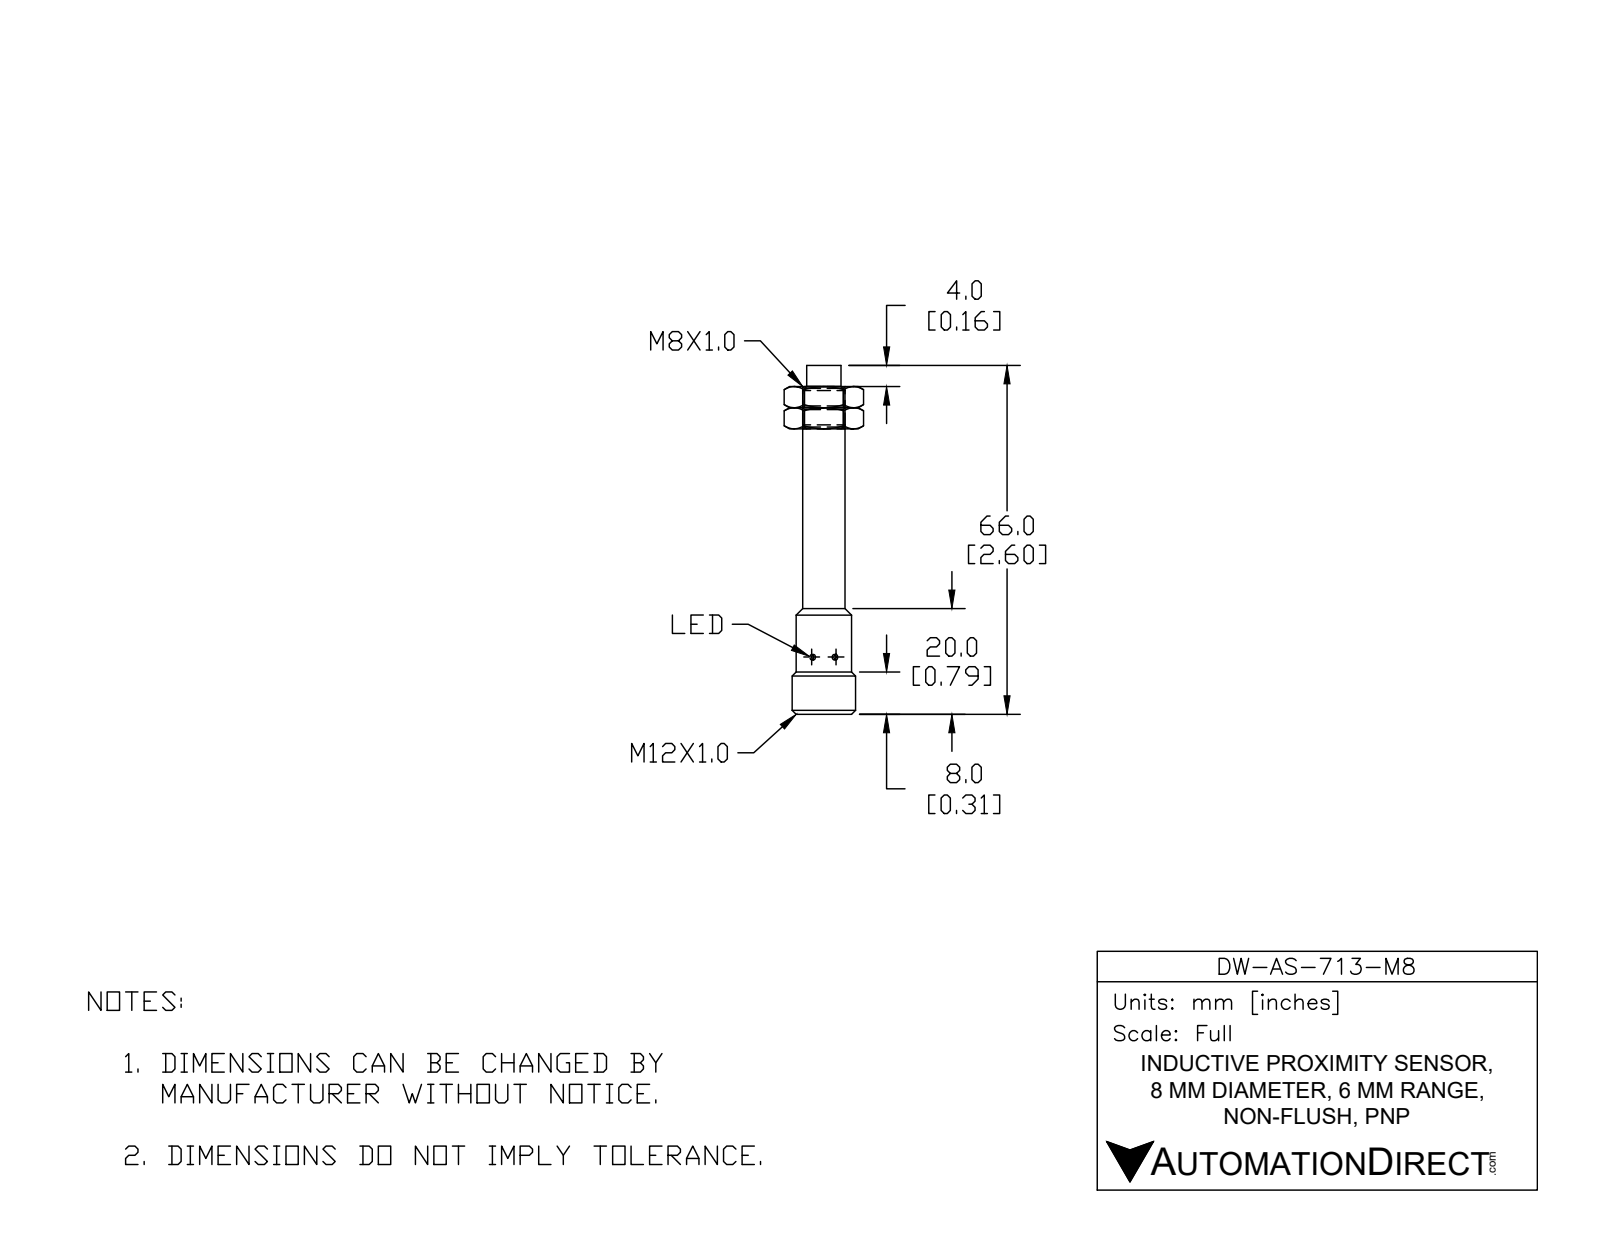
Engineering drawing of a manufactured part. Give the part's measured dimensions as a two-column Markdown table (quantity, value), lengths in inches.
| quantity | value |
| --- | --- |
| part name | DW-AS-713-M8 |
| STEP written by | SolidWorks 2017 (AUTOMOTIVE_DESIGN) |
| units | inches |
| bodies | 1 solid, 43 faces (7 planar, 26 cylindrical, 10 other) |
| overall size | 2.598 × 0.472 × 0.472 |
| volume | 0.218 in³ |
| surface area | 3.895 in² |
| round holes (diameter × count) | 0.118 × 2, 0.335 × 1 |
| round bosses / shafts (diameter × count) | 0.039 × 4, 0.472 × 1, 0.415 × 1, 0.315 × 1, 0.256 × 1 |
| partial cylindrical surfaces (radius × count) | 0.02 × 2, 0.022 × 1, 0.183 × 1, 0.193 × 1 |
| main face-to-face distances | 0.343, 2.256, 2.598, 1.811, 0.445, 0.787, 0.043, 2.539, 0.728, 0.283 |
